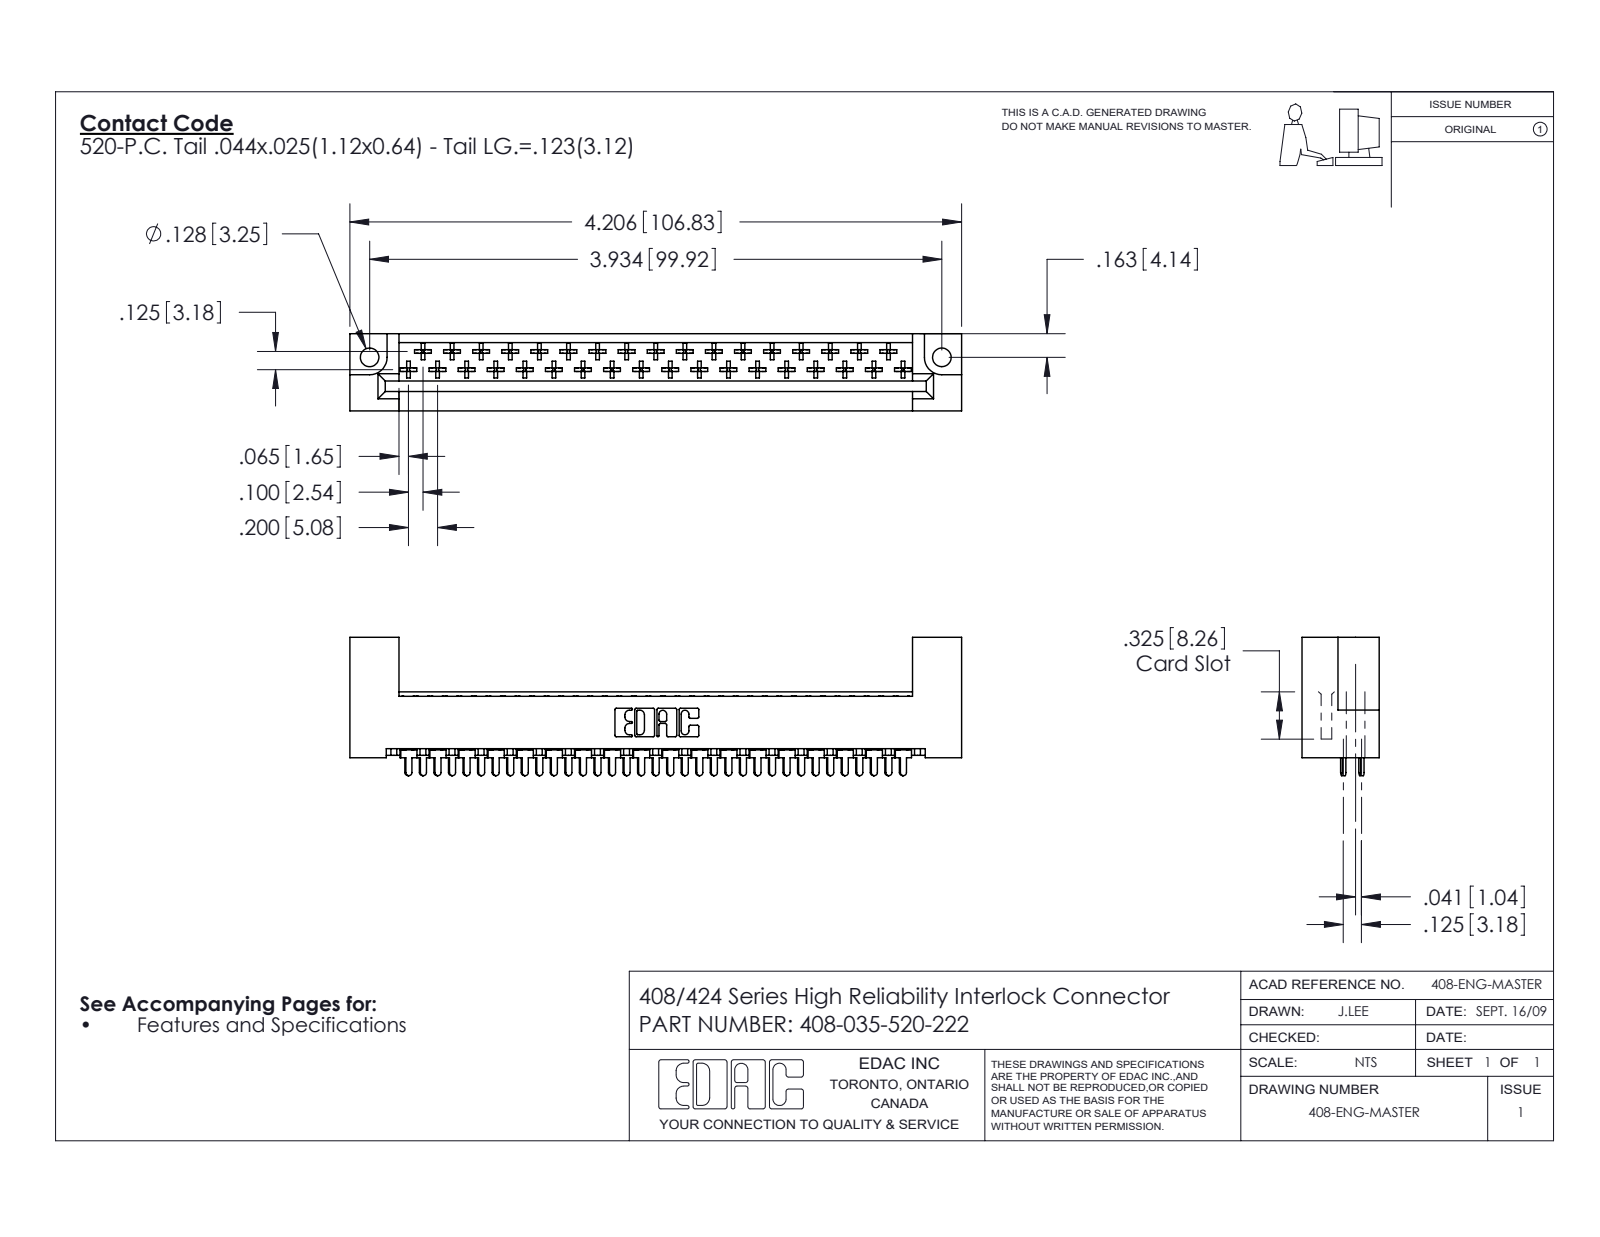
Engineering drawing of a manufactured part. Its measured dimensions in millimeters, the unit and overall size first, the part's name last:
Units: millimetres
Overall size (bounding box): 106.8 × 24.2 × 13.5
Round holes (diameter × count): ⌀3.3 ×2
Partial cylindrical surfaces — rounded edges, fillets, slot ends (radius × count): R0.3 ×210, R0.5 ×37, R0.6 ×35, R0.3 ×22, R0.2 ×6, R0.8 ×6, R0.7 ×3, R3 ×2
Main face-to-face distances: 13.5, 3.2, 2.5, 0.6, 0.6, 9.2, 6, 6.6, 10.1, 5.5
Hole centre spacings: 99.9
Volume: 13 300 mm³ · Surface area: 15 300 mm²
Bodies: 36 solids, 2064 faces (1559 planar, 365 cylindrical, 140 other)
Part name (STEP PRODUCT): 408 Part_035 - 2; 408-035-520-222; 408-290-001_408-290-120
STEP written by: SolidWorks 2016 (CONFIG_CONTROL_DESIGN)
